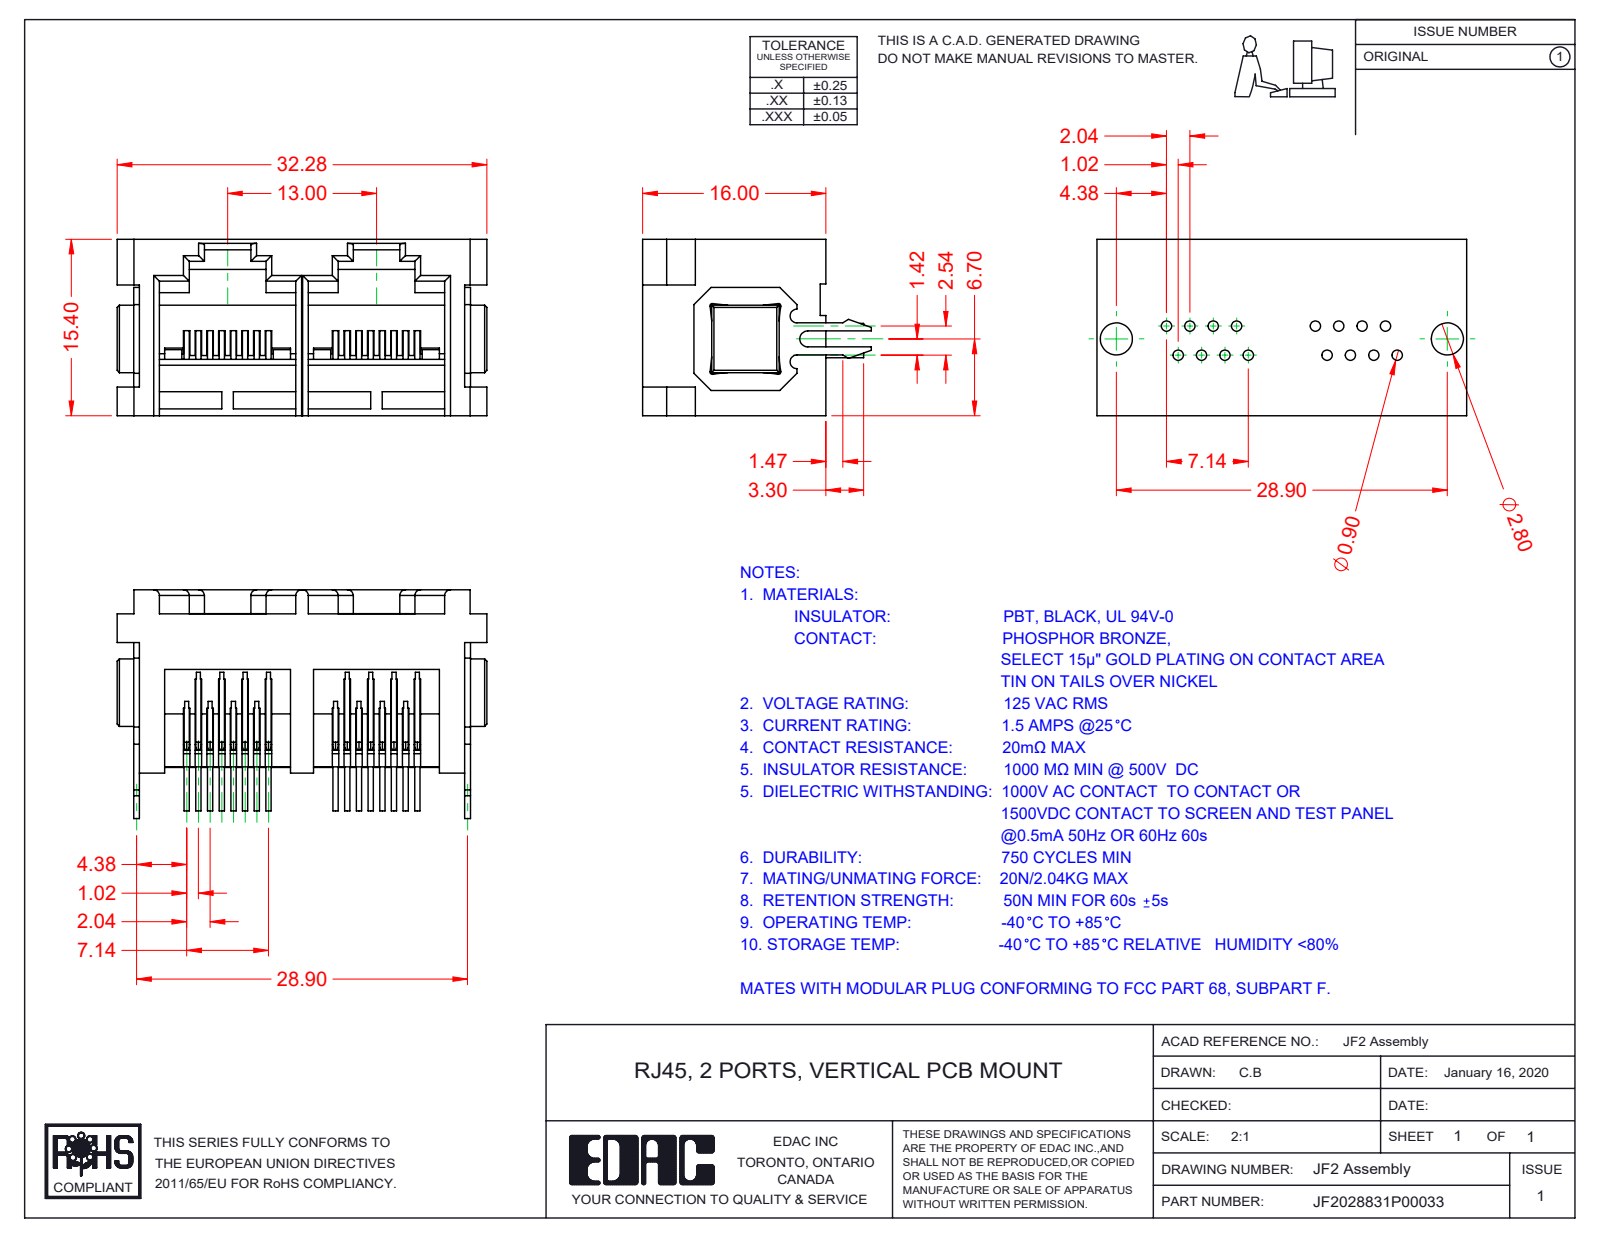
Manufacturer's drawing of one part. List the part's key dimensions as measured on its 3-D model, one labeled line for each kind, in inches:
Part name (STEP PRODUCT): F2 Contact Lock; F2 Boardlocks; F2 Insulator; F2 Contacts (+1 more)
STEP written by: SolidWorks 2016 (CONFIG_CONTROL_DESIGN)
Units: inches
Bodies: 21 solids, 1130 faces (734 planar, 300 cylindrical, 96 other)
Overall size (bounding box): 1.271 × 0.786 × 0.606
Volume: 0.215 in³ · Surface area: 10.71 in²
Round bosses / shafts (diameter × count): ⌀0.018 ×64
Partial cylindrical surfaces — rounded edges, fillets, slot ends (radius × count): R0.007 ×32, R0.02 ×15, R0.008 ×4, R0.801 ×4, R0.012 ×3, R0.024 ×2, R0.008 ×1, R0.018 ×1
Main face-to-face distances: 0.496, 0.083, 0.512, 0.059, 0.111, 0.036, 0.459, 0.02, 1.118, 0.433
